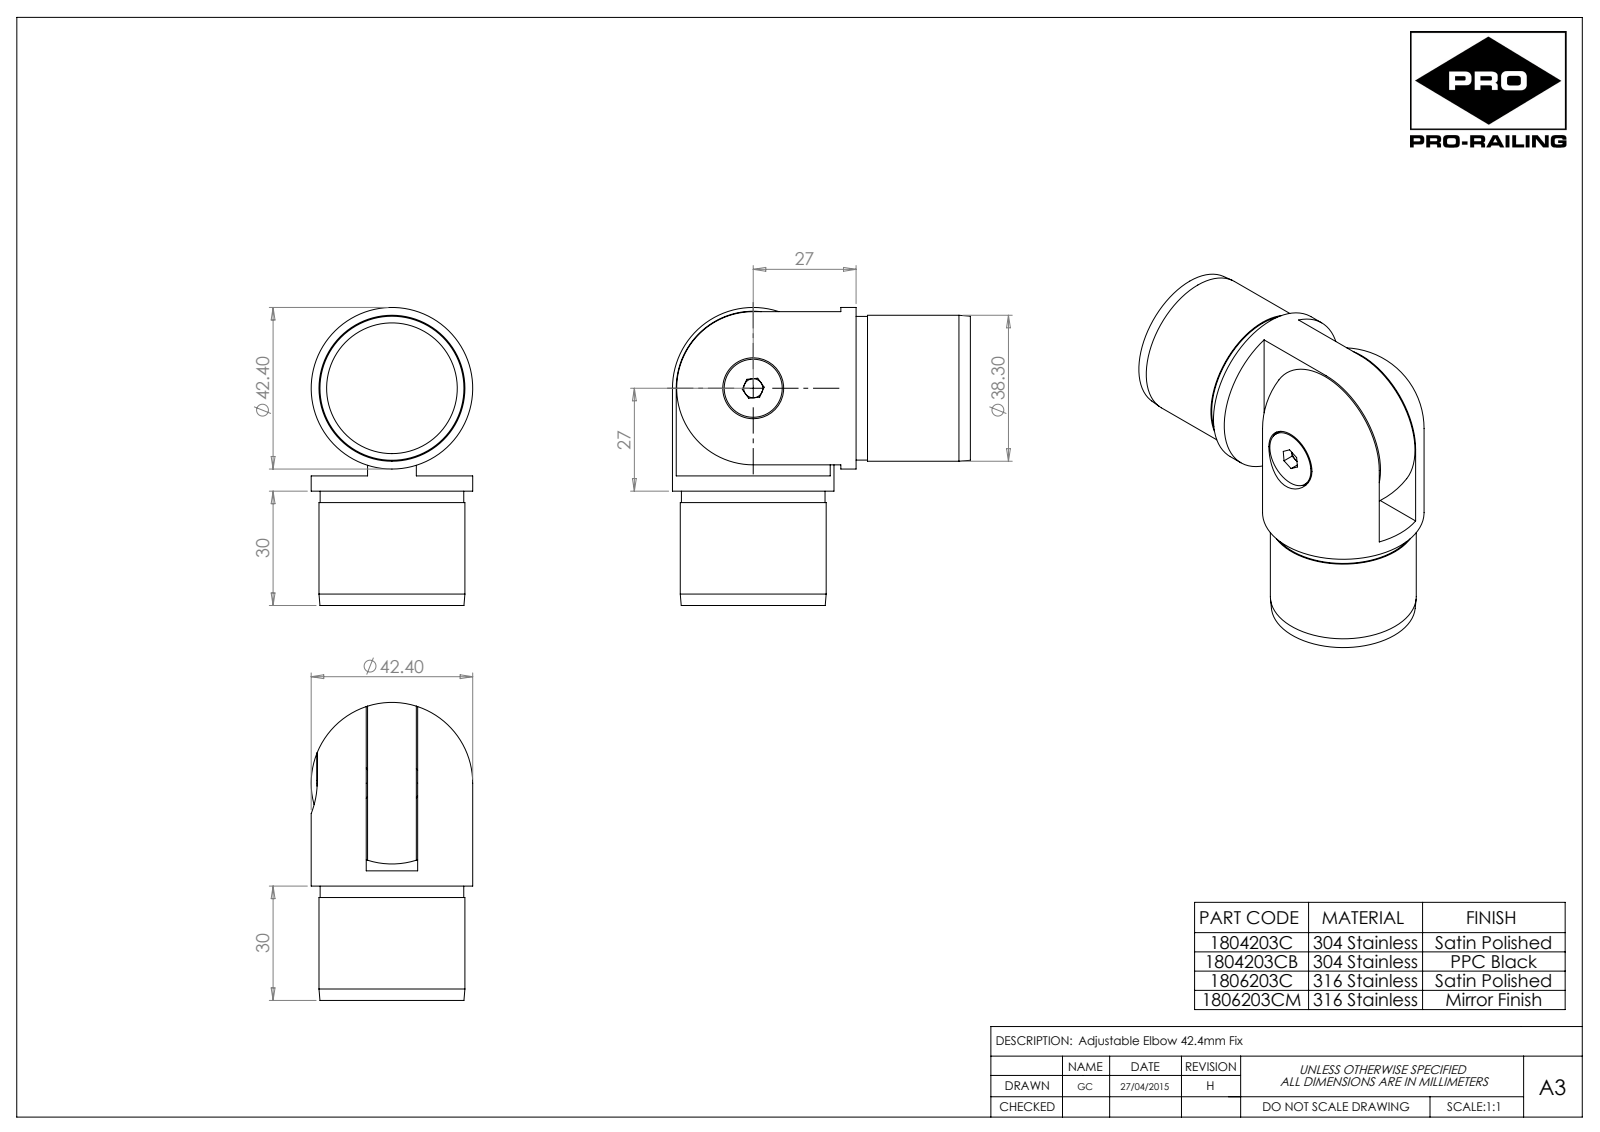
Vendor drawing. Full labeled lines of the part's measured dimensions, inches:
Part name (STEP PRODUCT): 1804203C Part2_defeature.STEP; 1804203C Part1_defeature.STEP; 1806203C; socket countersunk head screw_bsi_ISO 10642 - M8 x 30 --- 30S.STEP (+1 more)
STEP written by: SolidWorks 2018 (AUTOMOTIVE_DESIGN)
Units: inches
Bodies: 3 solids, 189 faces (29 planar, 60 cylindrical, 100 other)
Overall size (bounding box): 3.079 × 3.079 × 1.669
Volume: 7.518 in³ · Surface area: 41.88 in²
Round holes (diameter × count): ⌀0.276 ×1, ⌀0.323 ×1, ⌀0.63 ×1
Round bosses / shafts (diameter × count): ⌀1.669 ×2, ⌀1.508 ×2, ⌀1.484 ×2, ⌀0.6 ×1, ⌀0.315 ×1
Main face-to-face distances: 0.504, 1.339, 0.014, 0.518, 0.215, 0.228, 0.732, 0.746, 0.531, 1.181
